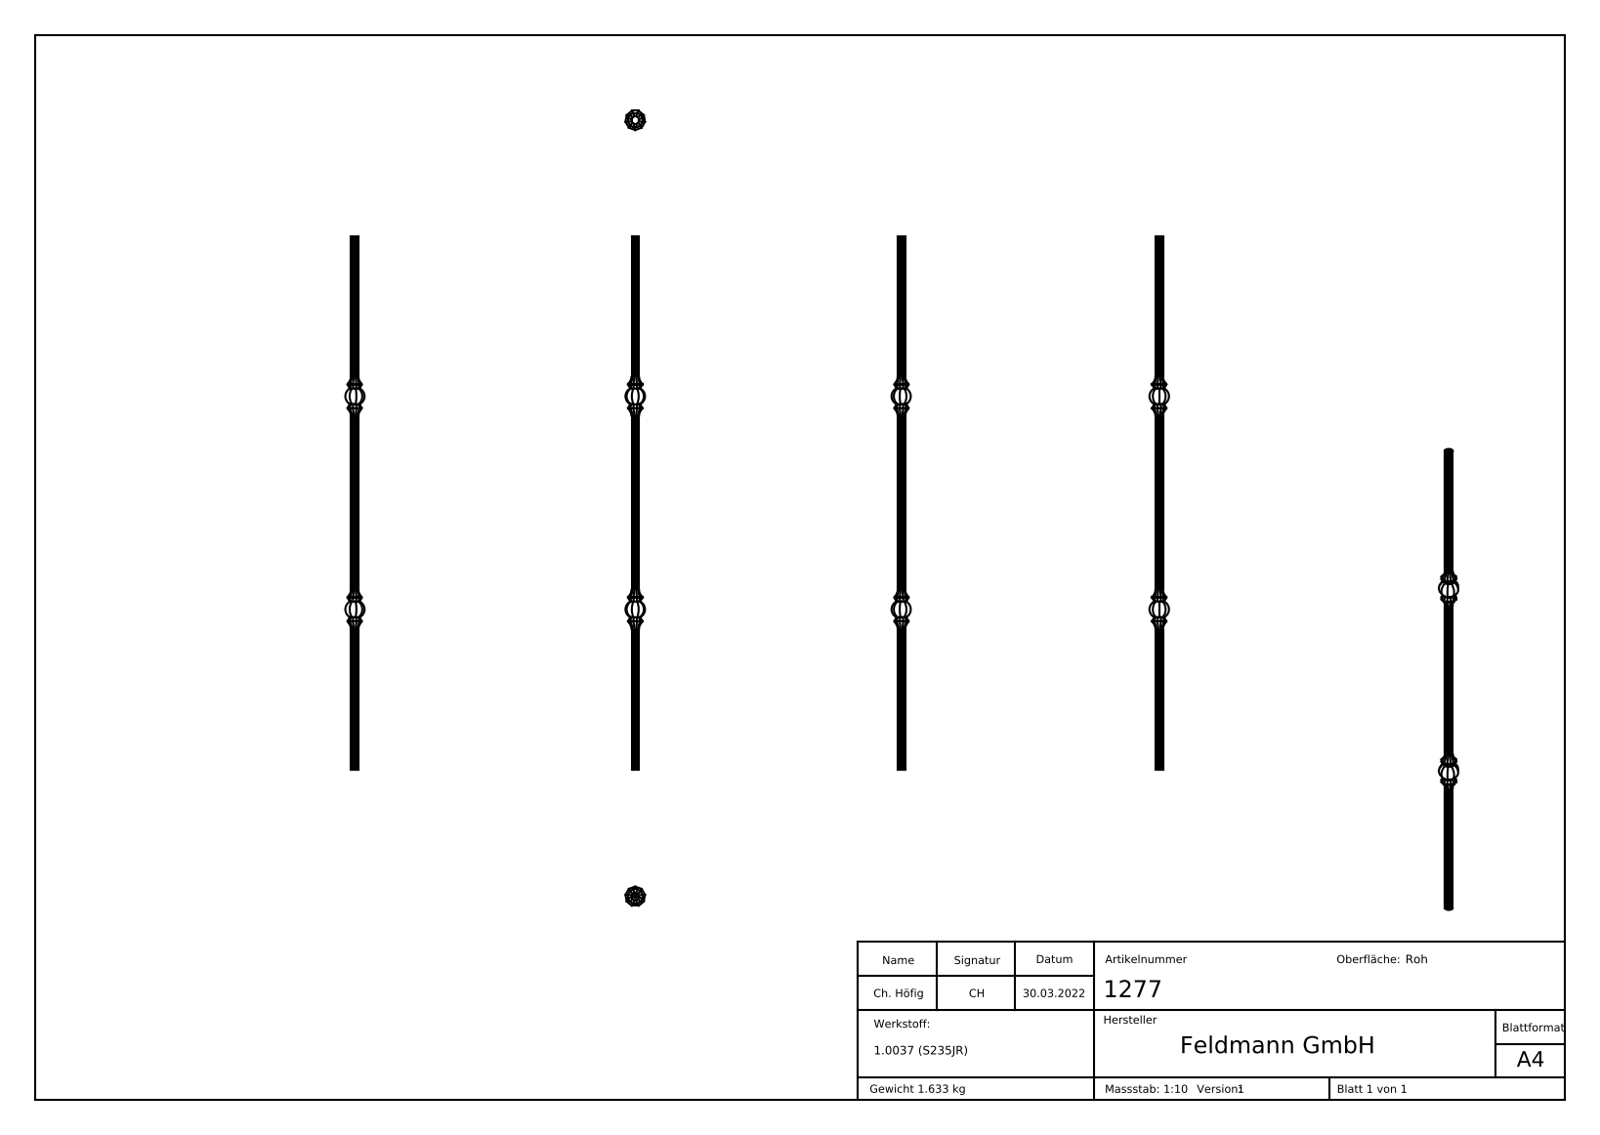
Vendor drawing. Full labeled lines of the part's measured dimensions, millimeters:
Part name (STEP PRODUCT): 1277
STEP written by: SolidWorks 2018 (CONFIG_CONTROL_DESIGN)
Units: millimetres
Bodies: 1 solid, 438 faces (298 planar, 18 cylindrical, 122 other)
Overall size (bounding box): 1000 × 36.68 × 36.12
Volume: 209 324 mm³ · Surface area: 52 072 mm²
Partial cylindrical surfaces — rounded edges, fillets, slot ends (radius × count): R17 ×18
Main face-to-face distances: 14, 207.6, 207.76, 207.44, 6.5, 20.5, 207.32, 207.88, 27, 1000
